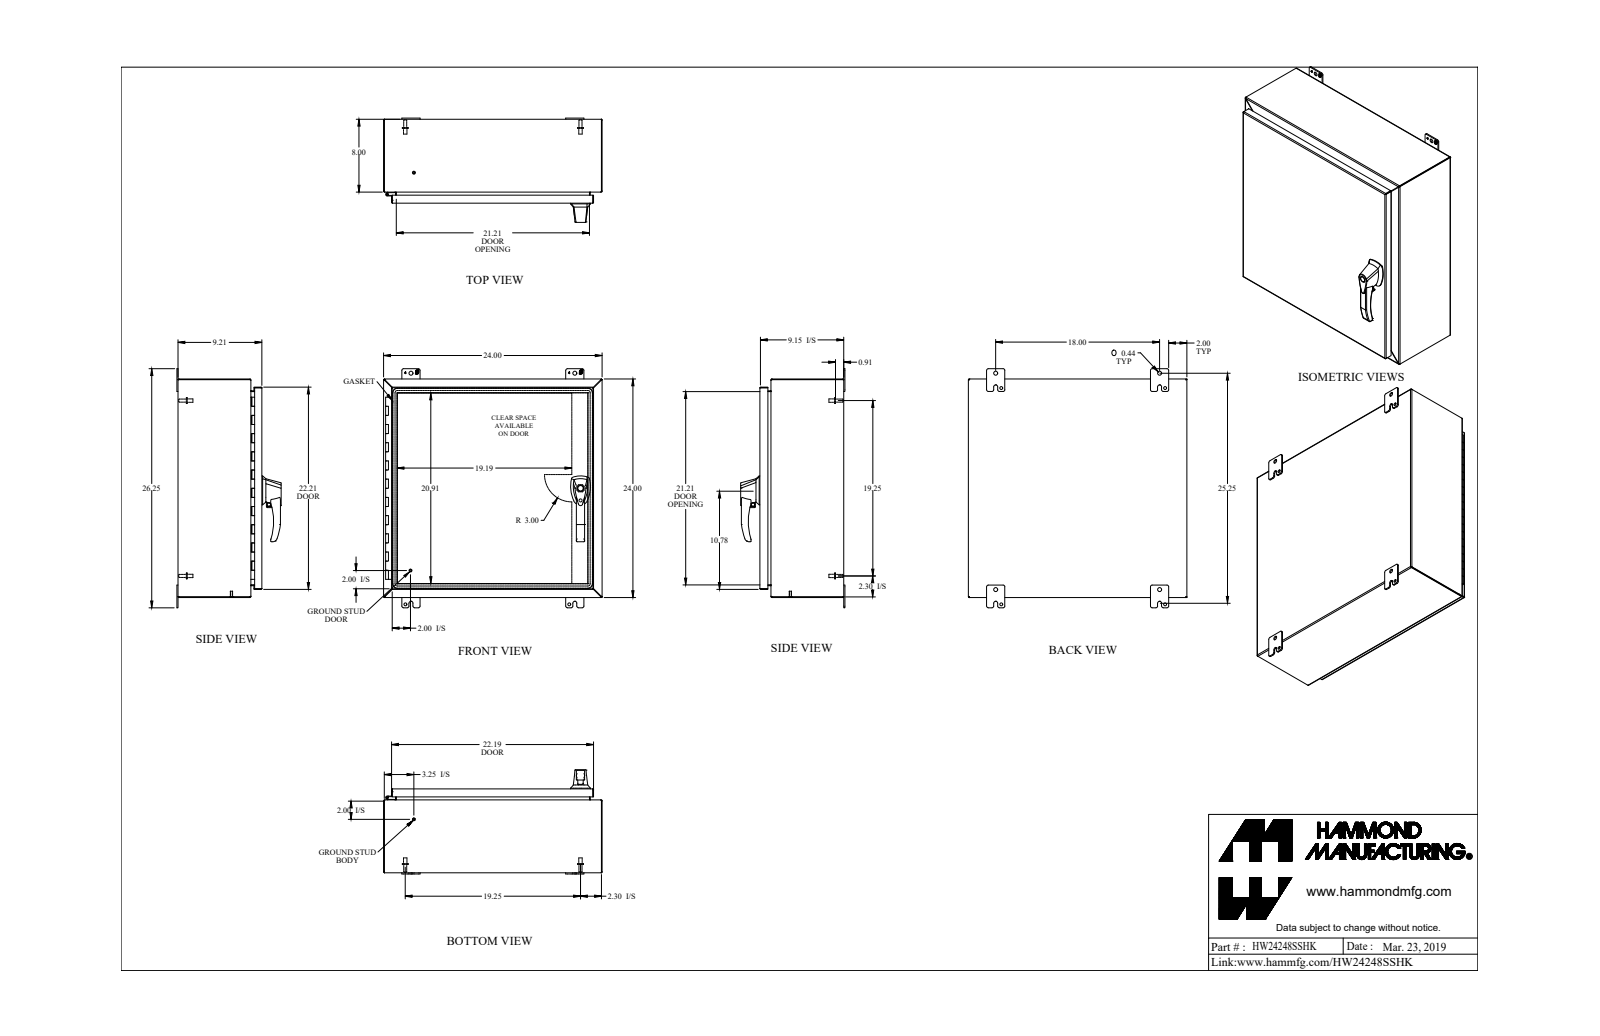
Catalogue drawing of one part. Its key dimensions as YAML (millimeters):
part_name: "HW24248SSHK"
step_written_by: "SolidWorks 2018 (AUTOMOTIVE_DESIGN)"
units: millimeters
bodies: {solids: 42, faces: 1423, planar: 699, cylindrical: 569, other: 155}
overall_size: [666.8, 609.6, 290.8]
volume: 3056000
surface_area: 3085000
round_holes:
  - {diameter: 4.5, count: 6}
  - {diameter: 8, count: 5}
  - {diameter: 6.4, count: 3}
  - {diameter: 6.7, count: 3}
  - {diameter: 10.5, count: 3}
  - {diameter: 5, count: 2}
  - {diameter: 6.5, count: 2}
  - {diameter: 10, count: 2}
  - {diameter: 11.1, count: 2}
  - {diameter: 4.7, count: 1}
  - {diameter: 5.9, count: 1}
  - {diameter: 8.4, count: 1}
round_bosses_or_shafts:
  - {diameter: 9.5, count: 9}
  - {diameter: 6.4, count: 7}
  - {diameter: 4, count: 6}
  - {diameter: 16.5, count: 4}
  - {diameter: 8.4, count: 4}
  - {diameter: 8, count: 4}
  - {diameter: 25.4, count: 3}
  - {diameter: 13, count: 3}
partial_cylinders:
  - {radius: 6.4, count: 27}
  - {radius: 4.8, count: 24}
  - {radius: 0.9, count: 20}
  - {radius: 2.7, count: 20}
  - {radius: 1.5, count: 12}
  - {radius: 3.2, count: 9}
  - {radius: 1.1, count: 8}
  - {radius: 5.5, count: 8}
face_to_face_distances: [1.8, 607.8, 1.8, 232.1, 230.3, 232.1, 233.9, 605.9, 609.6, 201.4]
hole_center_spacings: [28.2, 206.2, 206.2, 412.4, 34, 172.2, 192.4, 192.5]
